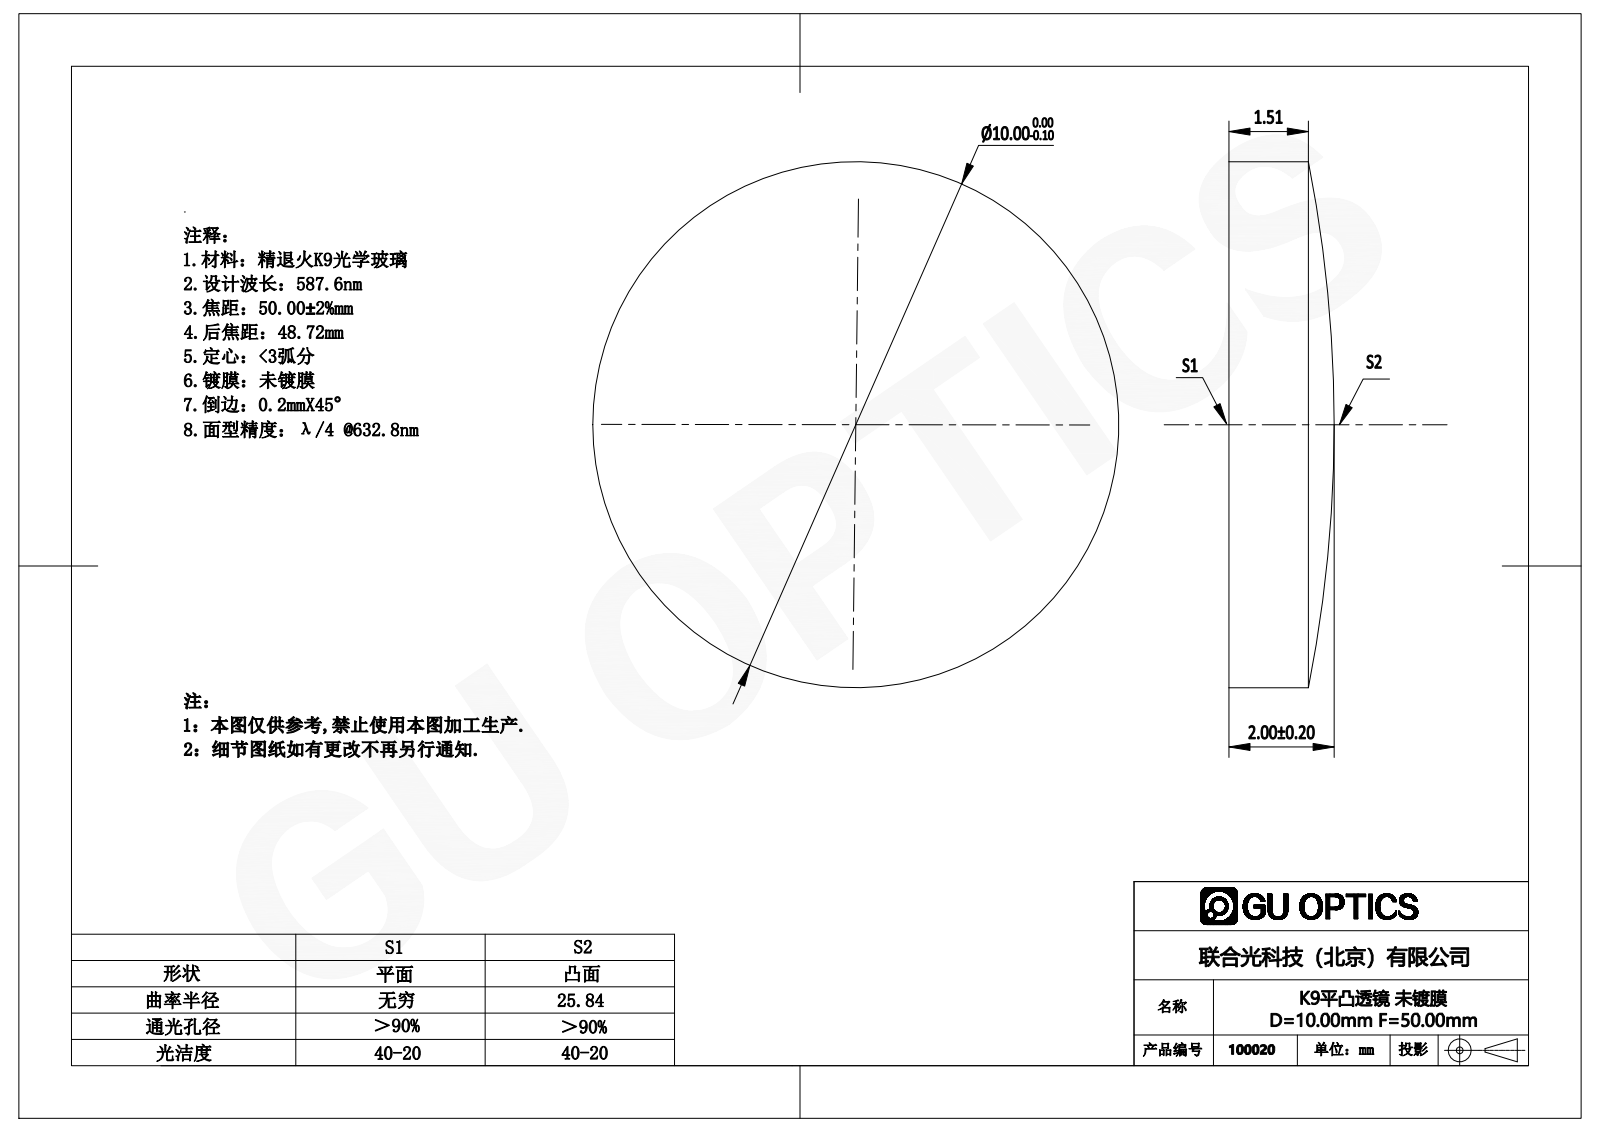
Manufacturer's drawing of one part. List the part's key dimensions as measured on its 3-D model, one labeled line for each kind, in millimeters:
Part name (STEP PRODUCT): 100020
STEP written by: SolidWorks 2016 (AUTOMOTIVE_DESIGN)
Units: millimetres
Bodies: 1 solid, 5 faces (1 planar, 2 cylindrical, 2 other)
Overall size (bounding box): 10 × 10 × 2
Volume: 138 mm³ · Surface area: 205 mm²
Round bosses / shafts (diameter × count): ⌀10 ×1
